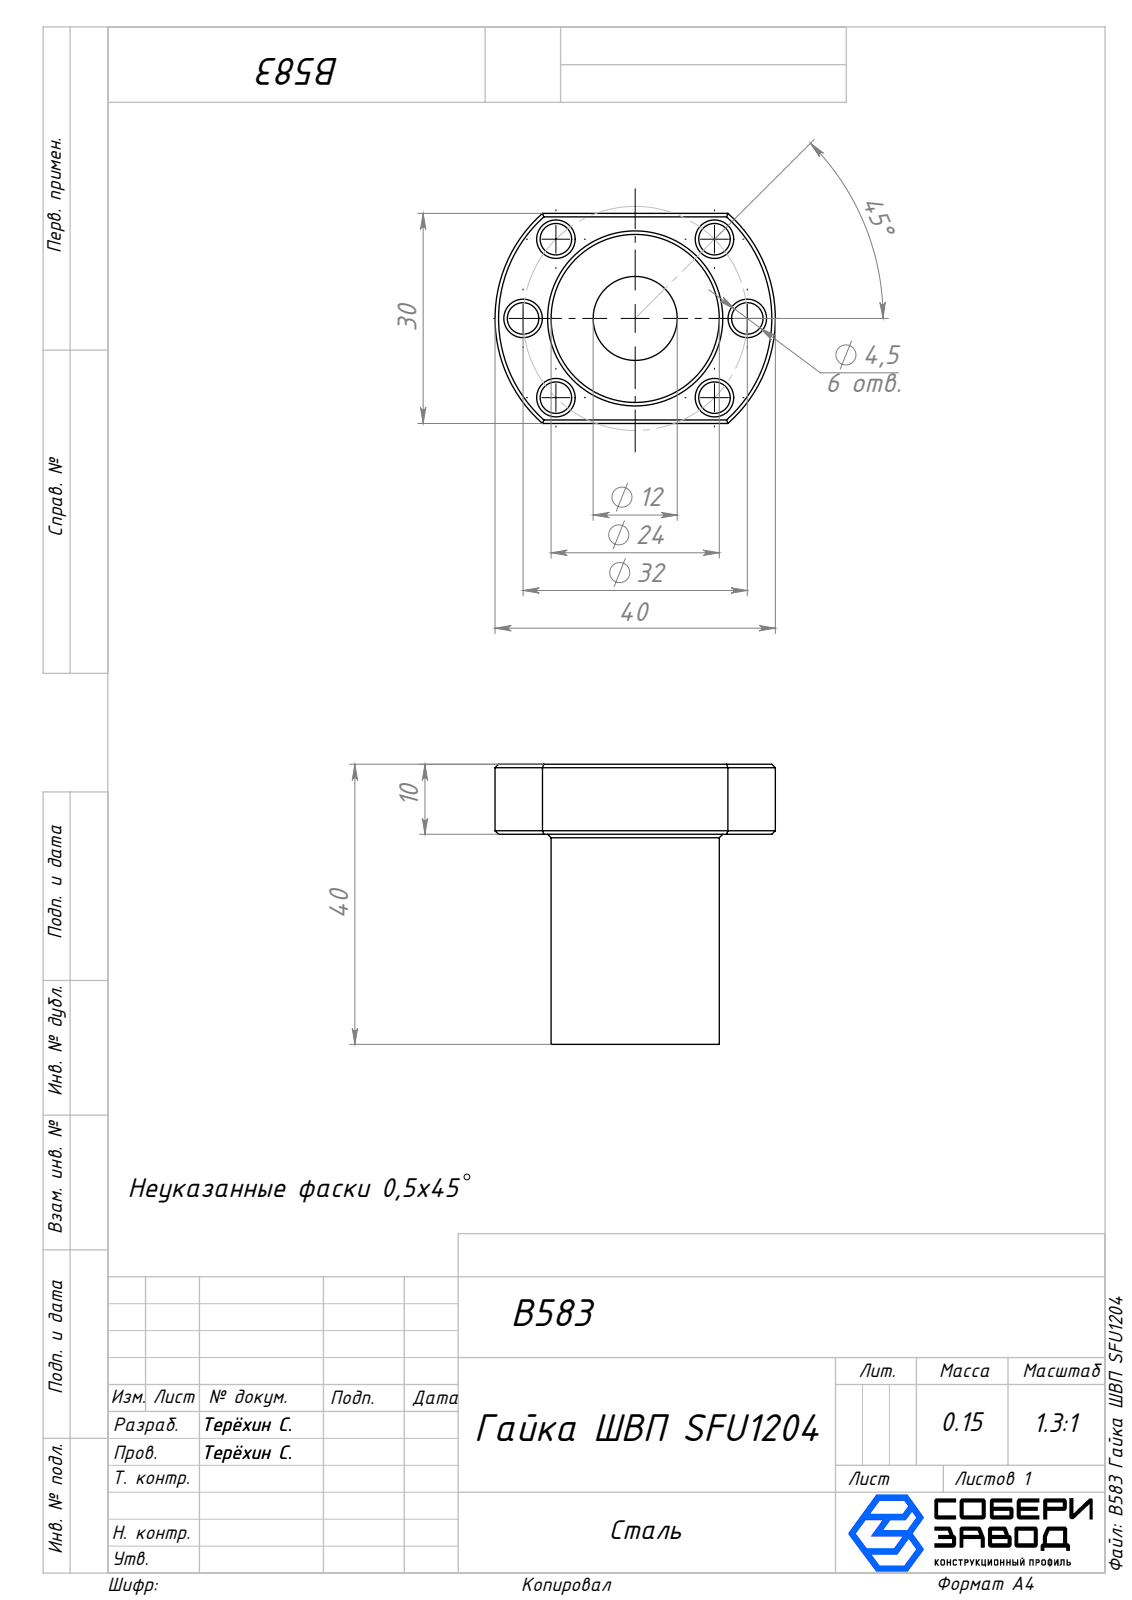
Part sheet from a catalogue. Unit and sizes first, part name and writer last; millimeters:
Units: millimetres
Overall size (bounding box): 40 × 40 × 30
Round holes (diameter × count): ⌀4.5 ×6, ⌀12 ×1
Round bosses / shafts (diameter × count): ⌀24 ×1
Partial cylindrical surfaces — rounded edges, fillets, slot ends (radius × count): R20 ×1
Main face-to-face distances: 30, 10, 40, 27.57
Hole centre spacings: 12.24, 15.99, 22.62, 29.56, 16, 31.99, 32
Volume: 18 799 mm³ · Surface area: 7 410 mm²
Bodies: 1 solid, 62 faces (9 planar, 19 cylindrical, 34 other)
Part name (STEP PRODUCT): B583 Гайка ШВП SFU1204
STEP written by: SolidWorks 2025 (AUTOMOTIVE_DESIGN)
